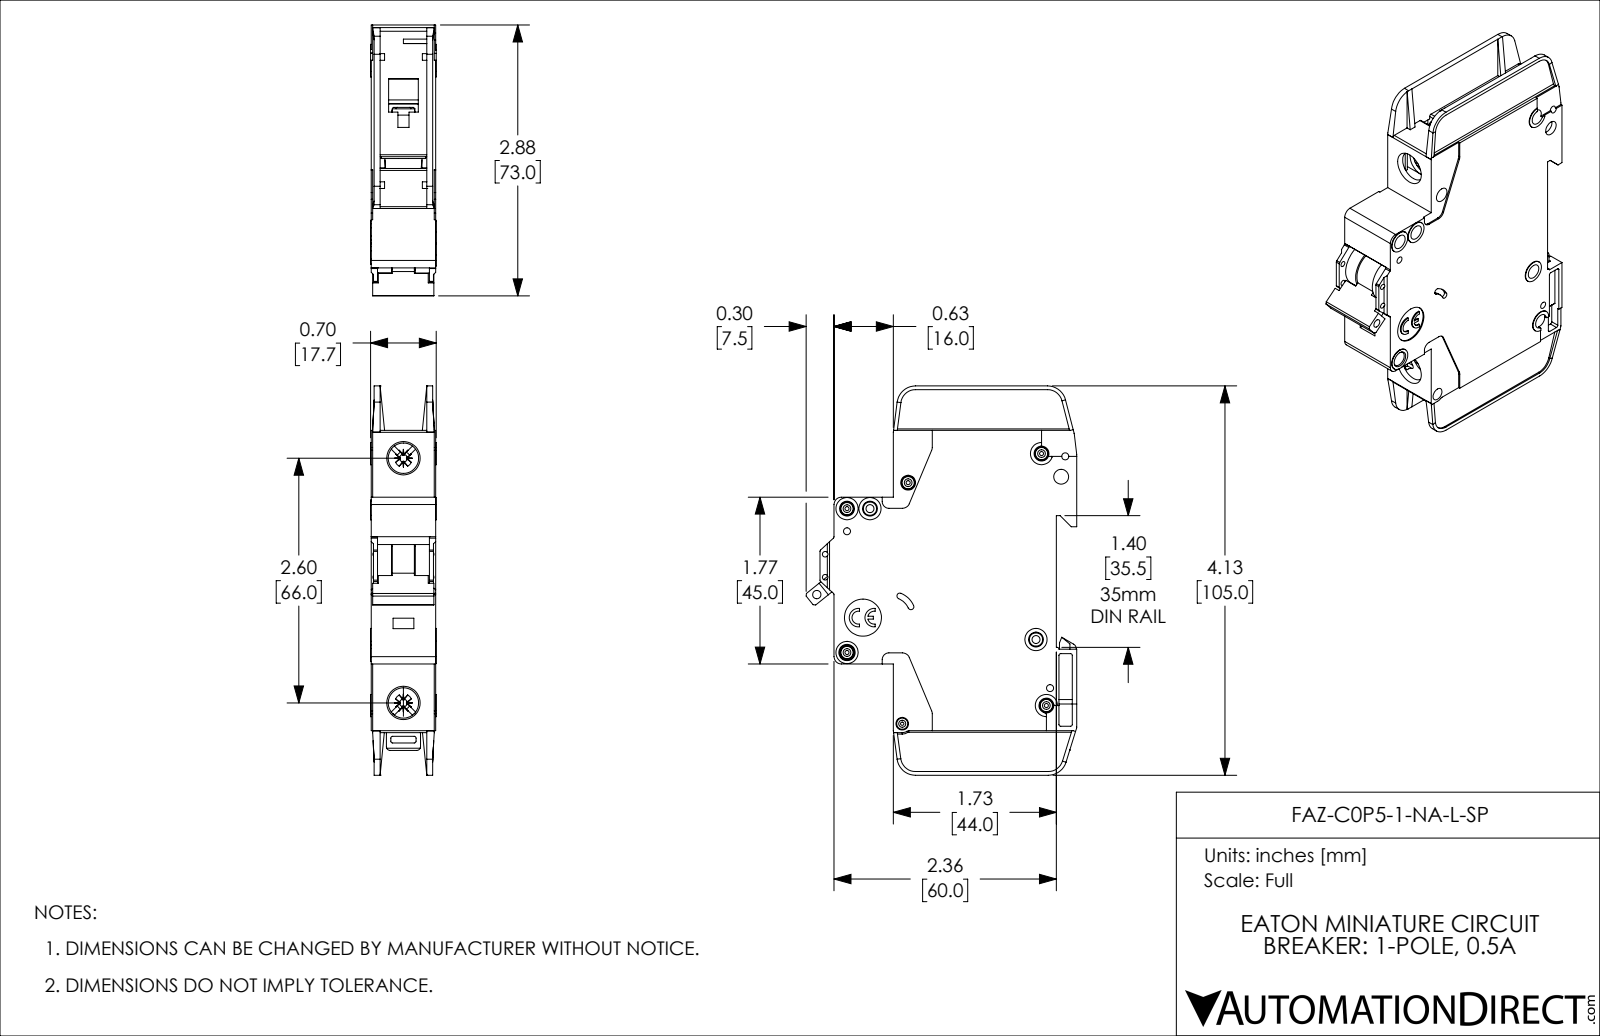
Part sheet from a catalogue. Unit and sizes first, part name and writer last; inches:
Units: inches
Overall size (bounding box): 4.134 × 2.876 × 0.697
Round holes (diameter × count): ⌀0.157 ×8, ⌀0.043 ×5, ⌀0.075 ×4, ⌀0.059 ×2, ⌀0.085 ×2, ⌀0.323 ×2, ⌀0.035 ×1, ⌀0.089 ×1, ⌀0.098 ×1, ⌀0.134 ×1, ⌀0.394 ×1
Round bosses / shafts (diameter × count): ⌀0.13 ×5, ⌀0.236 ×4, ⌀0.118 ×2, ⌀0.098 ×1
Partial cylindrical surfaces — rounded edges, fillets, slot ends (radius × count): R0.02 ×42, R0.016 ×10, R0.039 ×10, R0.079 ×8, R0.197 ×5, R0.008 ×4, R0.026 ×4, R0.043 ×4
Main face-to-face distances: 0.047, 0.685, 0.591, 0.638, 0.094, 0.543, 0.016, 0.031, 0.496, 0.575
Hole centre spacings: 0.244, 0.537, 0.87, 0.189, 0.199, 0.204, 0.221, 0.24
Volume: 4.682 in³ · Surface area: 41.01 in²
Bodies: 1 solid, 1127 faces (671 planar, 357 cylindrical, 99 other)
Part name (STEP PRODUCT): FAZ-C0P5-1-NA-L-SP
STEP written by: SolidWorks 2019 (AUTOMOTIVE_DESIGN)
